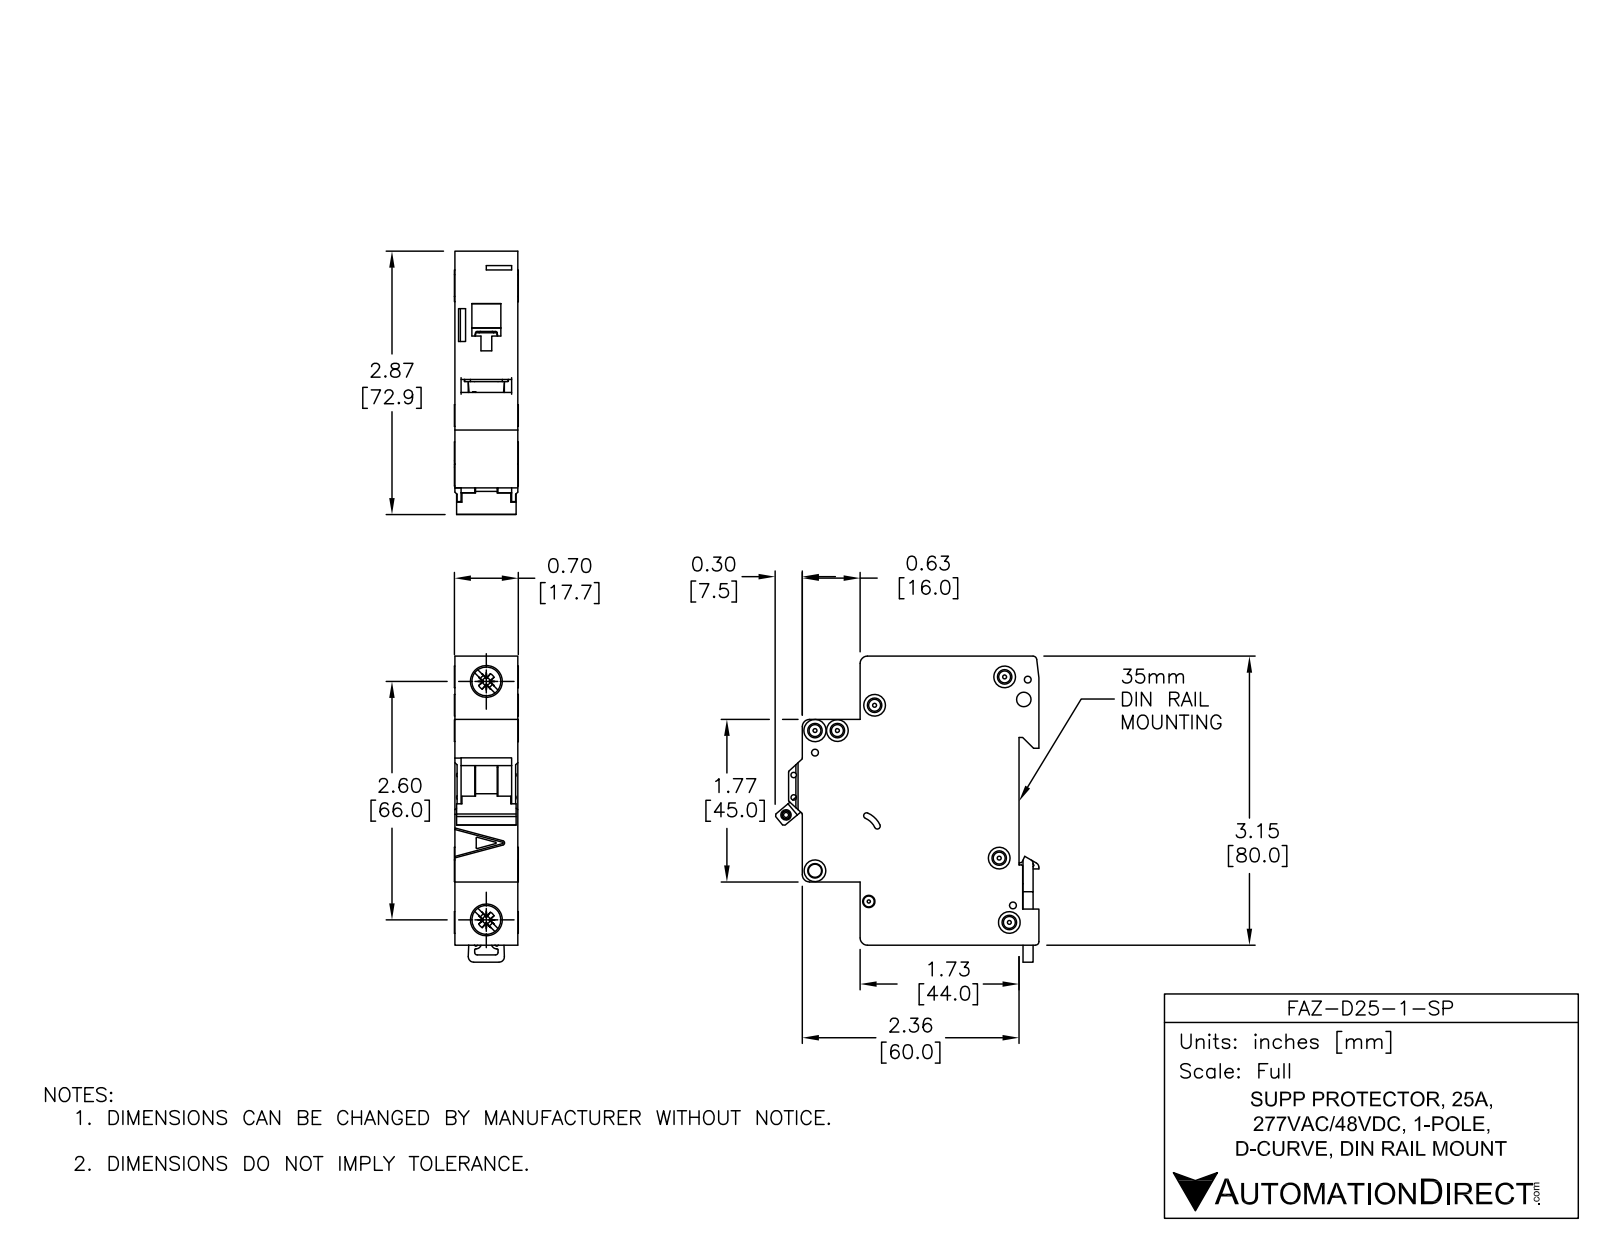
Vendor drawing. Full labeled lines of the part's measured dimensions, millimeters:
Part name (STEP PRODUCT): FAZ-D25-1-SP
STEP written by: SolidWorks 2014 (AUTOMOTIVE_DESIGN)
Units: millimetres
Bodies: 5 solids, 558 faces (235 planar, 202 cylindrical, 121 other)
Overall size (bounding box): 84.78 × 73.04 × 17.7
Volume: 74 935 mm³ · Surface area: 19 545 mm²
Round holes (diameter × count): ⌀3.6 ×6, ⌀1.9 ×3, ⌀1.09 ×2, ⌀1.5 ×2, ⌀4 ×2, ⌀7.15 ×2, ⌀2.15 ×1, ⌀2.2 ×1, ⌀2.55 ×1, ⌀3.3 ×1, ⌀3.4 ×1
Round bosses / shafts (diameter × count): ⌀6 ×4, ⌀8.2 ×2, ⌀2.5 ×1
Partial cylindrical surfaces — rounded edges, fillets, slot ends (radius × count): R0.25 ×30, R0.5 ×13, R2 ×8, R0.2 ×5, R1 ×4, R0.8 ×2, R3 ×2, R1.5 ×1
Main face-to-face distances: 17.5, 79.48, 5.5, 49.5, 44, 65.5, 60, 16, 1.75, 15.75
Hole centre spacings: 6.2, 13.64, 4.81, 5.19, 5.61, 6.1, 6.44, 8.19
